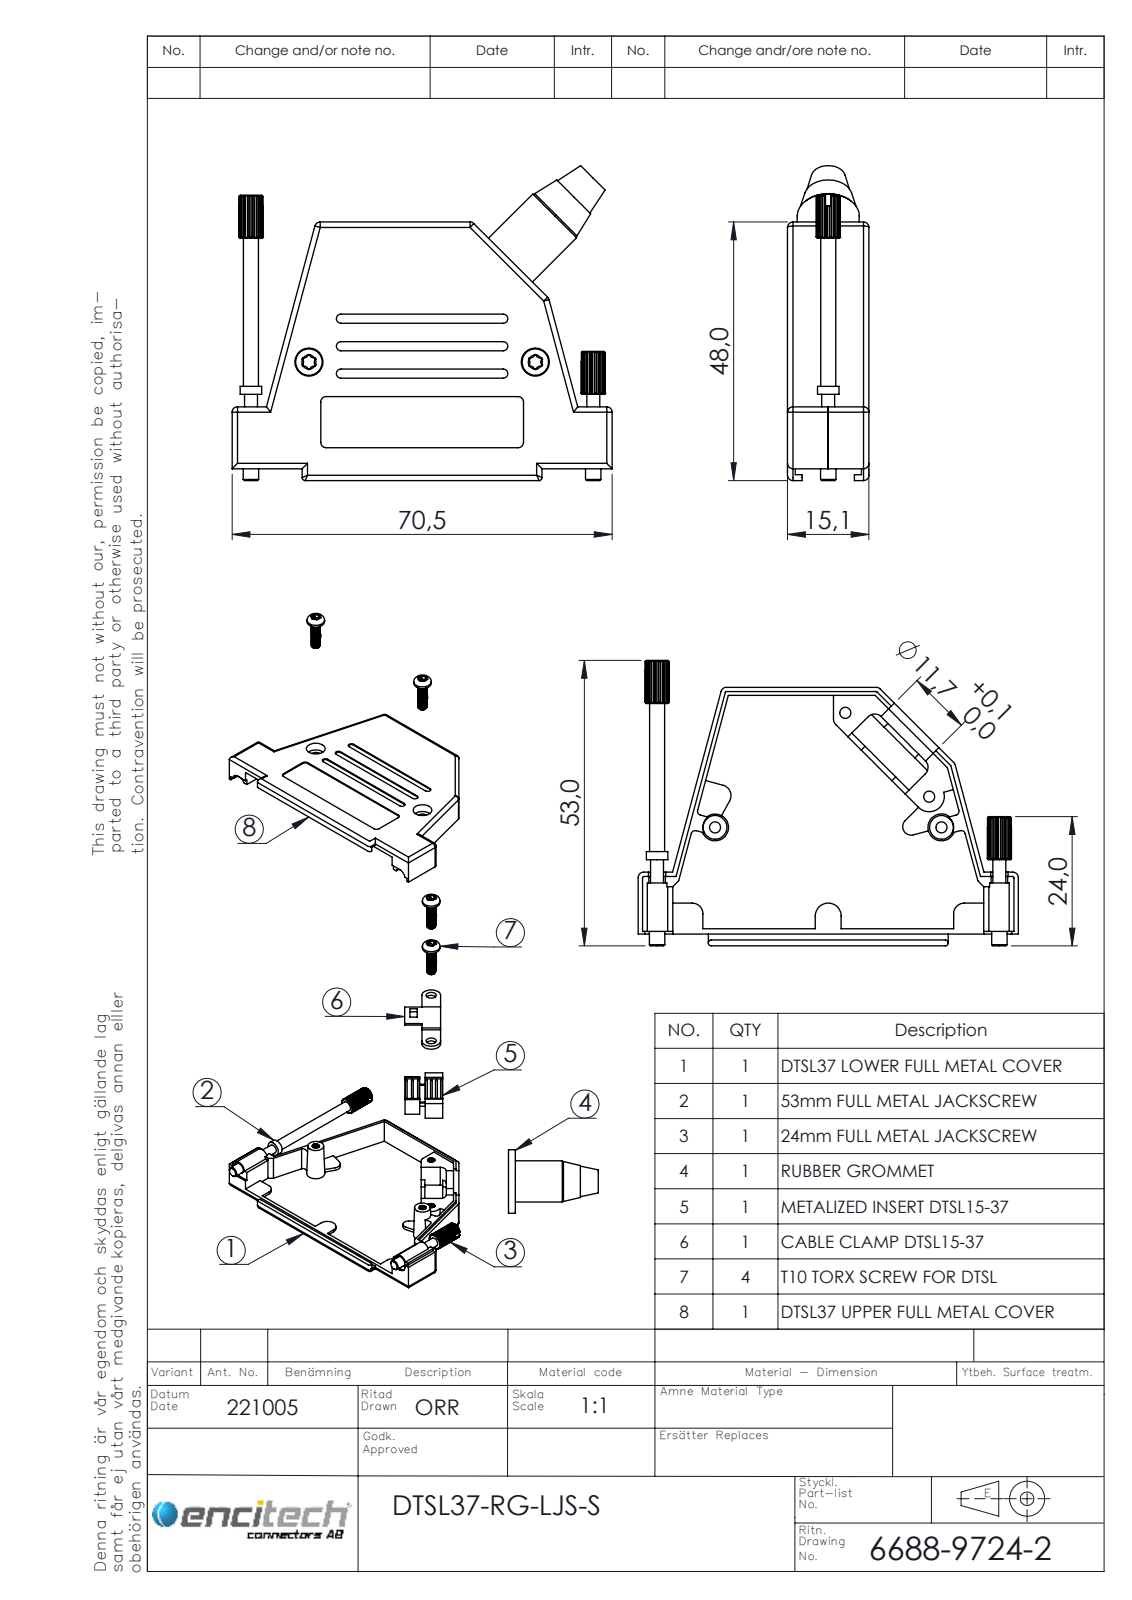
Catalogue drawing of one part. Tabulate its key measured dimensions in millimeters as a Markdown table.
| quantity | value |
| --- | --- |
| part name | 6805-0208-04; 6855-0119-02; 6844-0104-01; 6805-0208-14 (+5 more) |
| STEP written by | SolidWorks 2021 (AUTOMOTIVE_DESIGN) |
| units | millimeters |
| bodies | 15 solids, 1134 faces (447 planar, 579 cylindrical, 108 other) |
| overall size | 70.5 × 58.47 × 15.1 |
| volume | 13 932 mm³ |
| surface area | 19 942 mm² |
| round holes (diameter × count) | 2.05 × 4, 2.8 × 4, 3.1 × 2, 3.2 × 2, 5.2 × 2, 9 × 1, 11.7 × 1 |
| round bosses / shafts (diameter × count) | 4.9 × 4, 2.5 × 4, 7 × 2, 2.84 × 2, 2.4 × 2, 11.5 × 1, 11.1 × 1, 4 × 1 |
| partial cylindrical surfaces (radius × count) | 1 × 37, 0.18 × 24, 0.7 × 24, 0.85 × 12, 2 × 12, 0.3 × 4, 0.75 × 4, 0.2 × 2 |
| main face-to-face distances | 1.5, 13.6, 12.1, 15.1, 1.2, 14.8, 13.3, 6.05, 7.55, 7.25 |
| hole center spacings | 6.14, 22, 27.75, 32.19, 40.14, 42, 63.5 |
